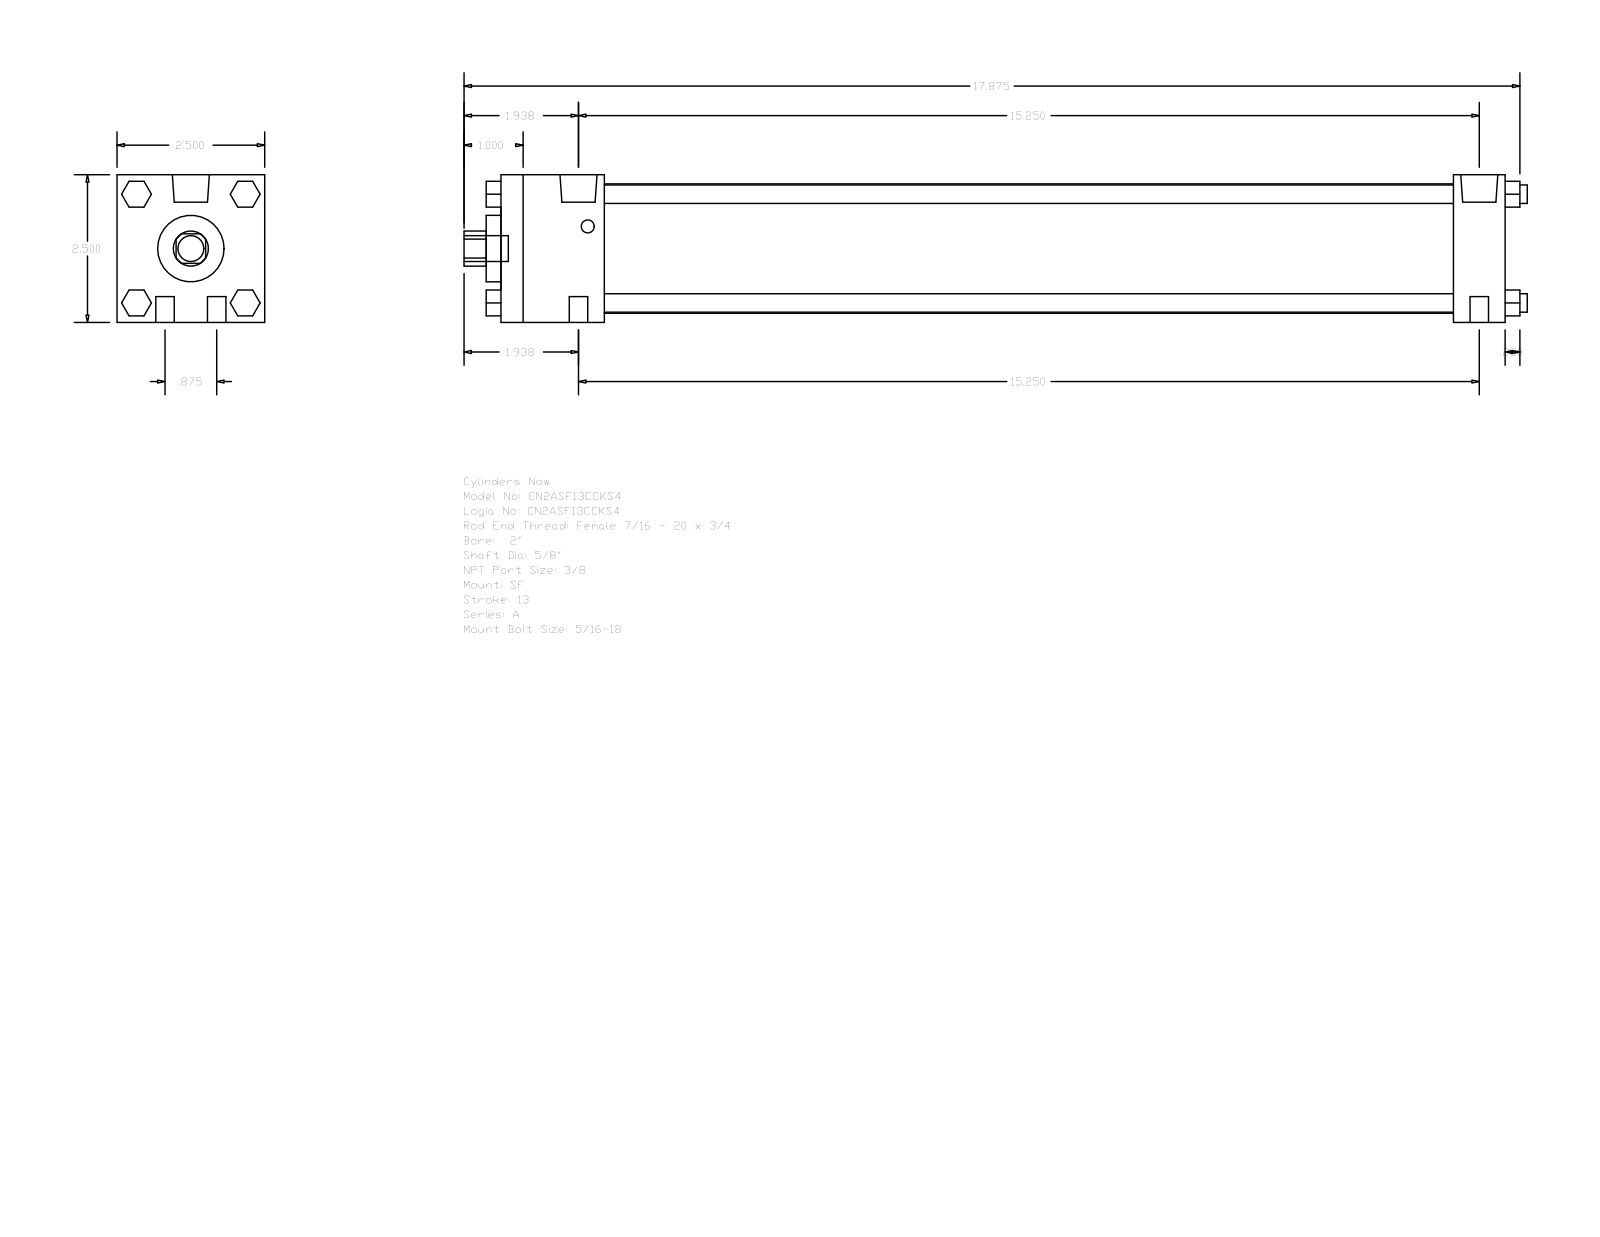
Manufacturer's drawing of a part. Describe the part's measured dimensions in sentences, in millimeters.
The part is named "A_SF__0200_0.625". Its 3-D file was written by "GSSL Pune (CONFIG_CONTROL_DESIGN)". It is 0 solids with 124 faces: 94 planar, 30 cylindrical and 0 other. Overall it measures 457.2 by 63.5 by 63.5 millimeters. Round holes: 1 of diameter 15.88, 1 of diameter 28.57, 1 of diameter 55.63. Round bosses or shafts: 8 of diameter 7.94, 2 of diameter 15.93, 2 of diameter 5.56, 1 of diameter 11.11. Partial cylindrical surfaces (rounded edges, fillets, slot ends): 1 of radius 7.54. The main face-to-face distances are 63.5, 431.8, 409.57, 22.23, 44.45, 365.12, 387.35, 50.8, 438.15, 6.35.
